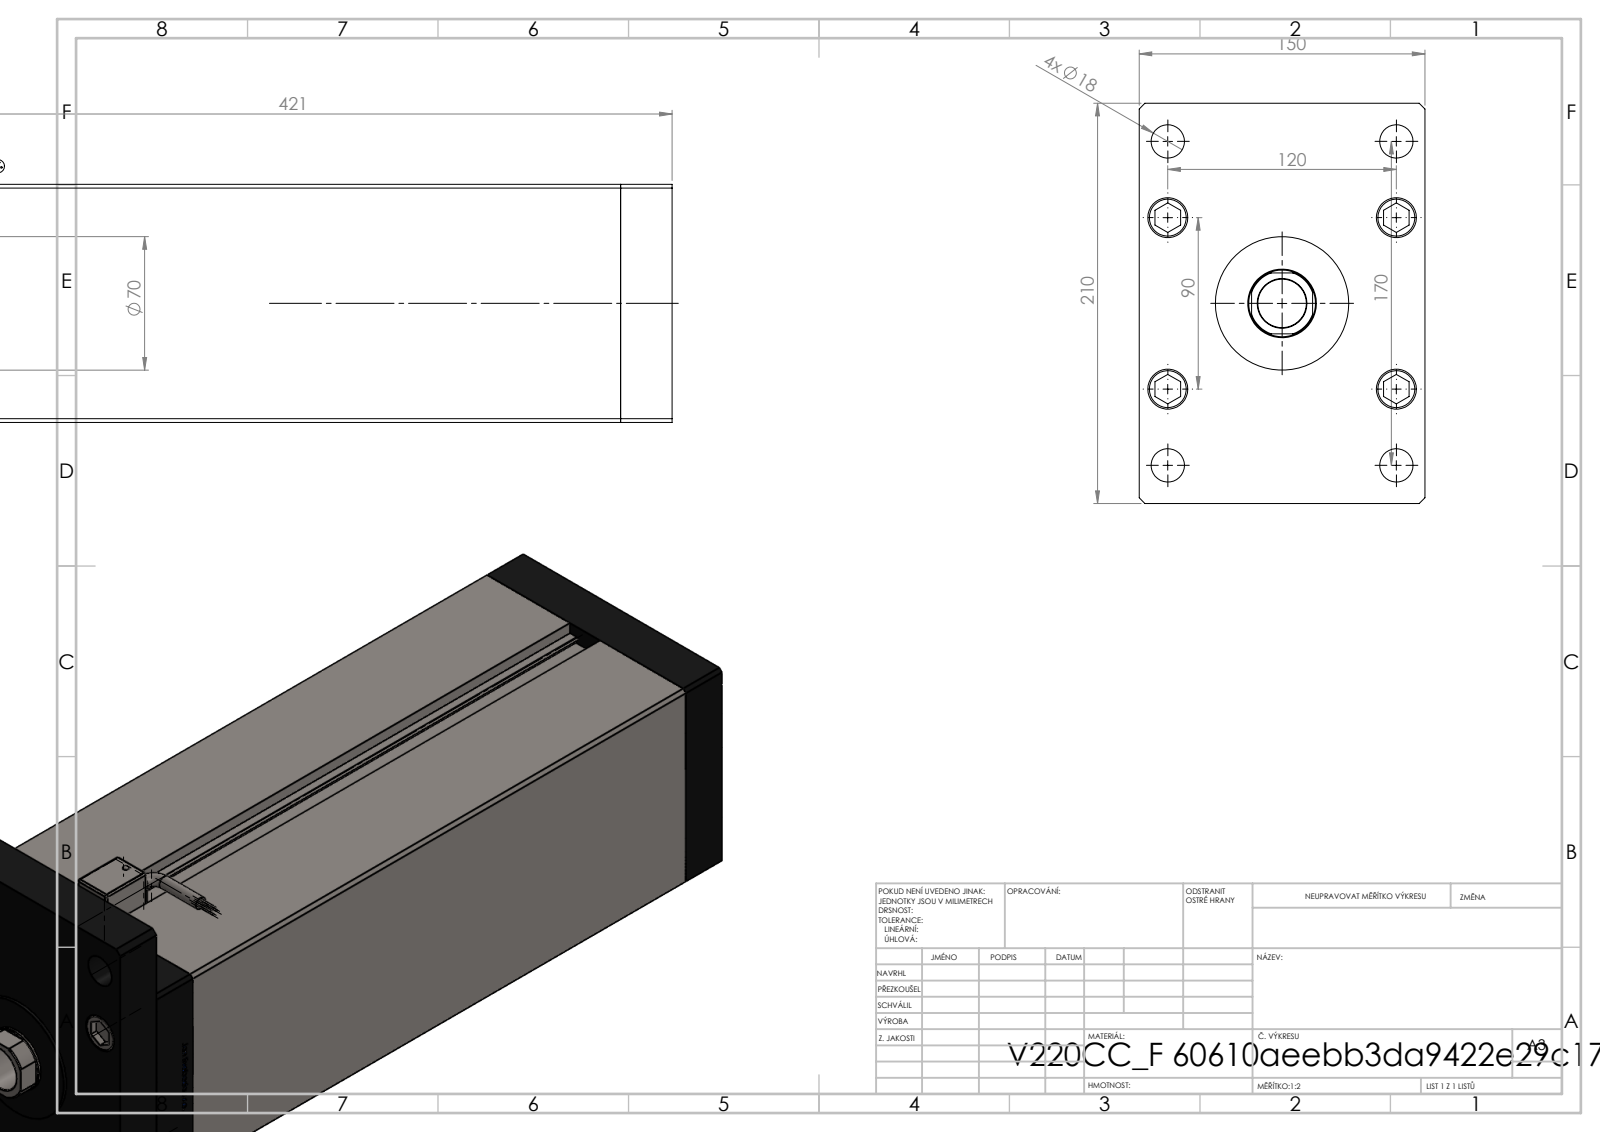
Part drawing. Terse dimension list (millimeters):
name: V220C_F_MIDDLE; V220C BACK_F; ALLEN BOLT; V220C_FRONT_F (+3 more)
written by: SolidWorks 2019 (CONFIG_CONTROL_DESIGN)
unit: mm
bodies: 20 solids, 1400 faces (552 planar, 224 cylindrical, 624 other)
size: 463 × 210 × 150
volume: 7 294 000 mm³; area: 663 267 mm²
holes: 9× ⌀17.5, 5× ⌀22, 4× ⌀16, 4× ⌀21, 1× ⌀3.6, 1× ⌀5, 1× ⌀7, 1× ⌀25.5, 1× ⌀36, 1× ⌀37.5
bosses: 9× ⌀8, 5× ⌀21, 4× ⌀0.85, 2× ⌀7, 1× ⌀80, 1× ⌀70, 1× ⌀6, 1× ⌀3.5
rounds: 14× R1, 2× R0.93, 2× R4, 1× R17.5
face distances: 27, 150, 125, 394, 421, 54, 367, 448, 6.5, 33.5
hole spacings: 51, 40, 75, 104.04, 120, 126.49, 130, 176.92
